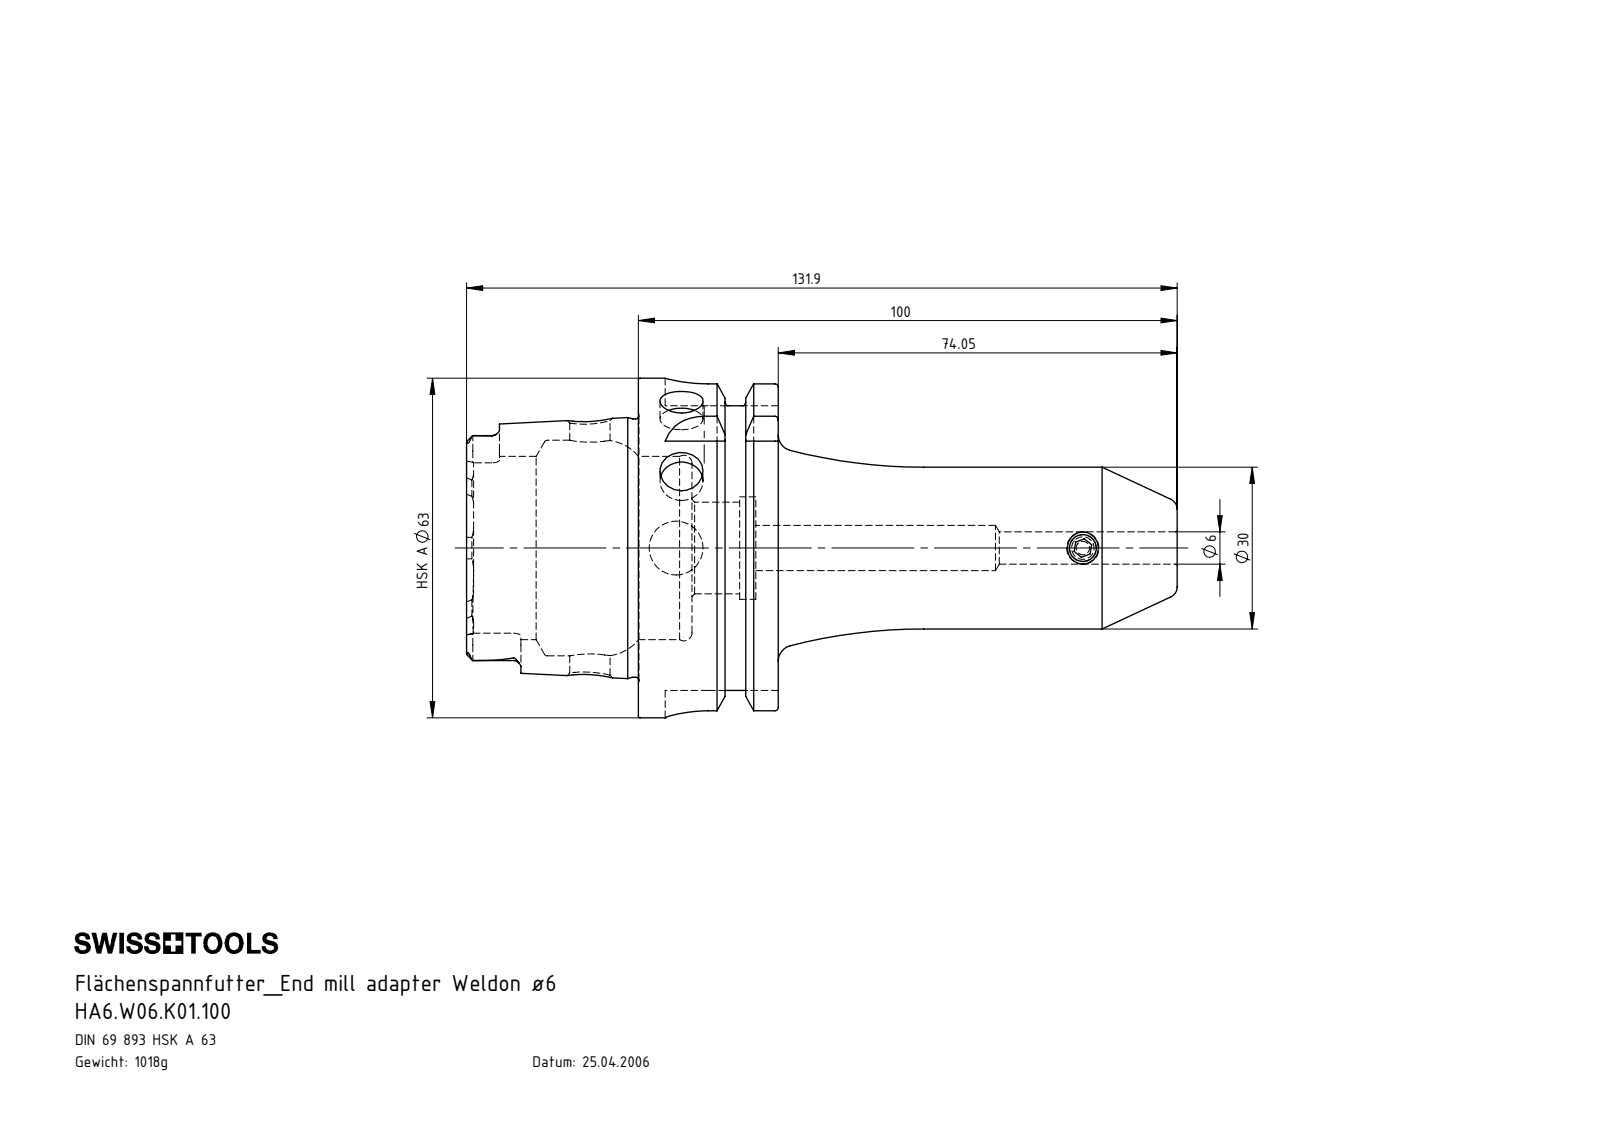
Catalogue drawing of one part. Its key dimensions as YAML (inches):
part_name: "HA6-W06.K01.100; W06-ER1.001.010; HA6-W06.K01.100_B_Fertigbearbeitung"
step_written_by: "SolidWorks 2012 (AUTOMOTIVE_DESIGN)"
units: inches
bodies: {solids: 2, faces: 203, planar: 57, cylindrical: 55, other: 91}
overall_size: [5.193, 2.48, 2.48]
volume: 7.917
surface_area: 47.54
round_holes:
  - {diameter: 0.315, count: 2}
  - {diameter: 0.197, count: 1}
  - {diameter: 0.236, count: 1}
  - {diameter: 0.295, count: 1}
  - {diameter: 0.331, count: 1}
  - {diameter: 0.394, count: 1}
  - {diameter: 0.669, count: 1}
  - {diameter: 0.748, count: 1}
  - {diameter: 1.339, count: 1}
  - {diameter: 1.575, count: 1}
round_bosses_or_shafts:
  - {diameter: 2.48, count: 1}
  - {diameter: 2.163, count: 1}
  - {diameter: 1.887, count: 1}
  - {diameter: 1.181, count: 1}
  - {diameter: 0.236, count: 1}
partial_cylinders:
  - {radius: 0.055, count: 6}
  - {radius: 0.113, count: 4}
  - {radius: 0.315, count: 4}
face_to_face_distances: [1.022, 0.63, 0.392, 1.256, 1.648, 2.278, 2.079, 0.858, 0.467, 2.114]
hole_center_spacings: [2.972]
